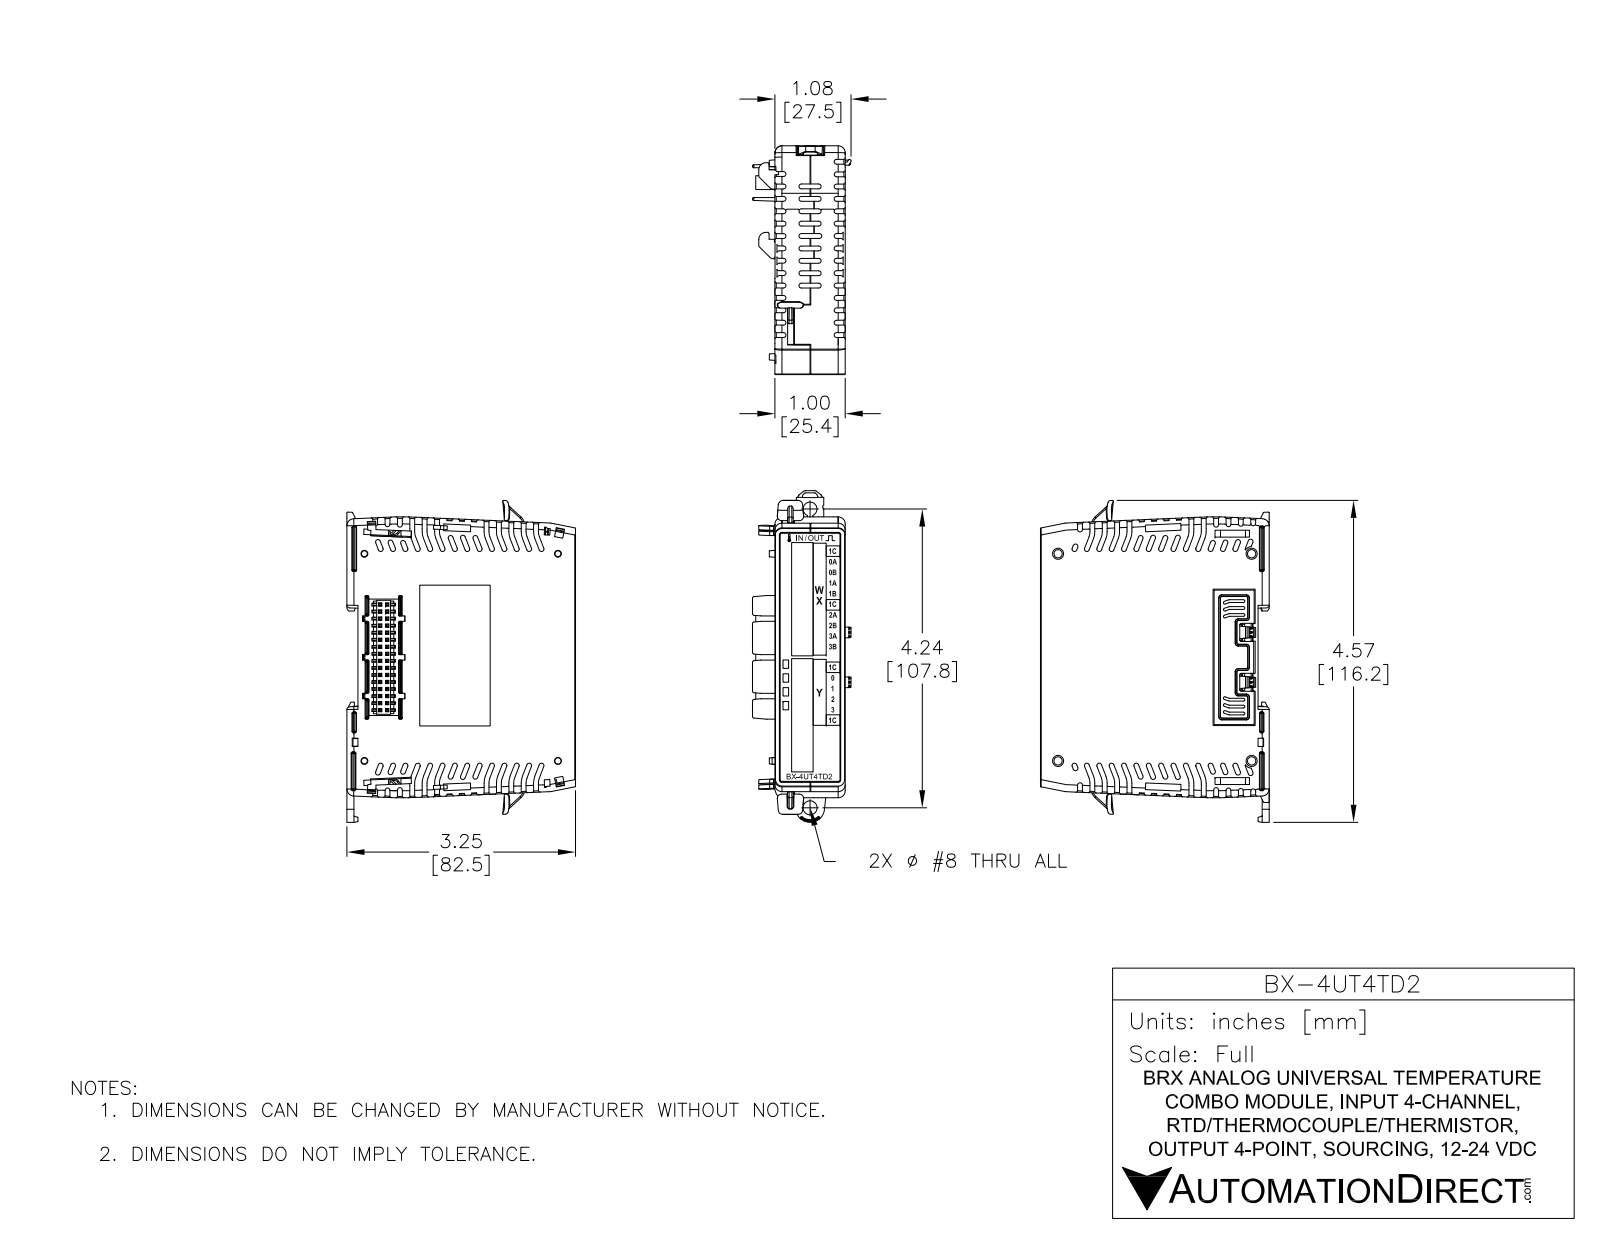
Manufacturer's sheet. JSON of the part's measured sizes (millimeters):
{"part_name": "BX-4UT4TD2", "step_written_by": "SolidWorks 2017 (AUTOMOTIVE_DESIGN)", "units": "millimeters", "bodies": {"solids": 16, "faces": 4180, "planar": 2931, "cylindrical": 672, "other": 577}, "overall_size": [116.5, 82.6, 35.6], "volume_mm3": 189800, "surface_area_mm2": 46780, "round_holes": [[1.2, 2], [1.7, 2], [3, 2], [3, 2], [1, 1], [5.1, 1]], "round_bosses_or_shafts": [[1.6, 2], [1.5, 2], [1.1, 1], [0.9, 1]], "partial_cylinders_radius": [[0.1, 102], [0.2, 101], [0.3, 47], [0.5, 34], [0.1, 24], [1.6, 20], [3, 14], [1, 13]], "face_to_face_distances": [25.4, 81.6, 81.8, 12.1, 1, 4, 77.5, 77.8, 2, 2.5], "hole_center_spacings": [2.5, 20.9, 23.3, 33, 53.2, 55.7, 65.7, 66.5]}
